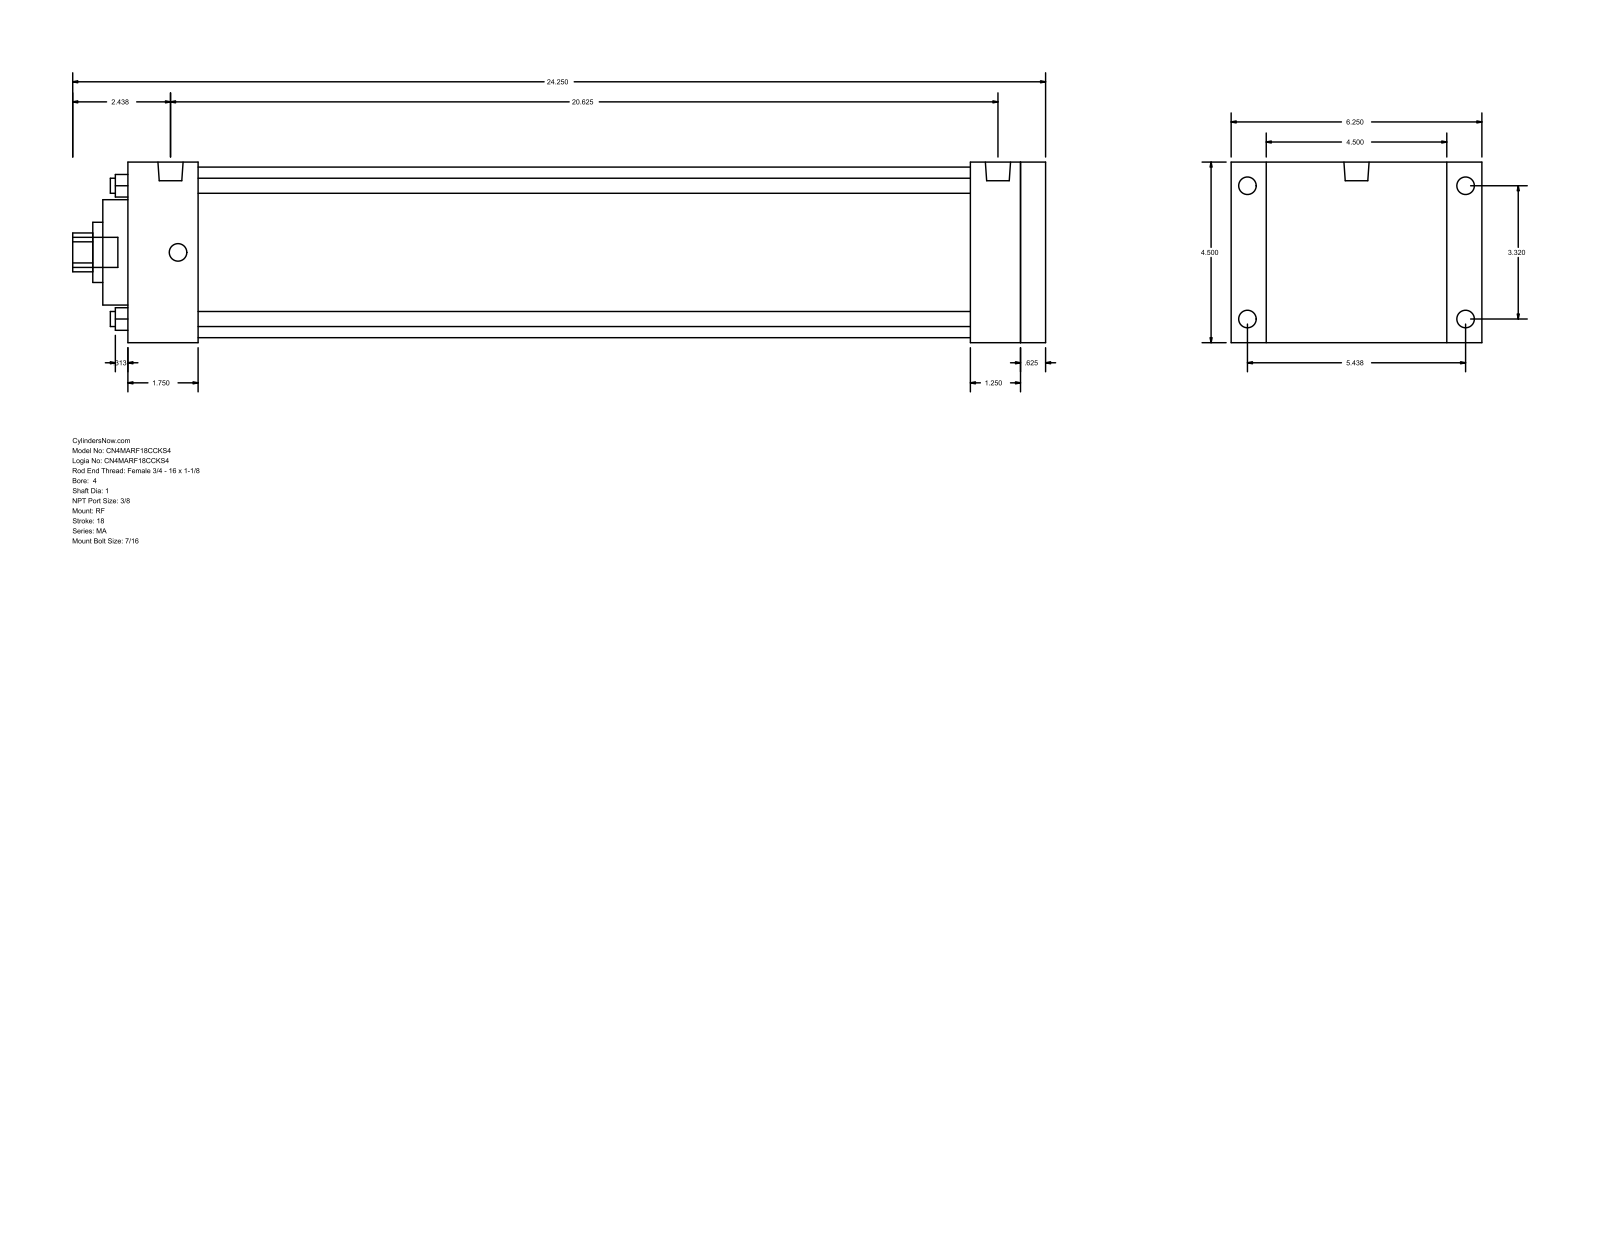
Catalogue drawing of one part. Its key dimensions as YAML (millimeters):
part_name: "MA_RF__0400_1"
step_written_by: "GSSL Pune (CONFIG_CONTROL_DESIGN)"
units: millimeters
bodies: {solids: 0, faces: 94, planar: 65, cylindrical: 29, other: 0}
overall_size: [615.95, 158.75, 114.3]
round_holes:
  - {diameter: 9.53, count: 4}
  - {diameter: 25.4, count: 1}
  - {diameter: 38.1, count: 1}
  - {diameter: 66.67, count: 1}
  - {diameter: 107.95, count: 1}
round_bosses_or_shafts:
  - {diameter: 11.11, count: 8}
  - {diameter: 15.93, count: 2}
  - {diameter: 19.05, count: 1}
partial_cylinders:
  - {radius: 12.29, count: 1}
face_to_face_distances: [114.3, 581.03, 15.87, 565.16, 22.23, 136.53, 533.41, 31.75, 47.62, 44.46]
hole_center_spacings: [59.62, 84.32, 119.25]
